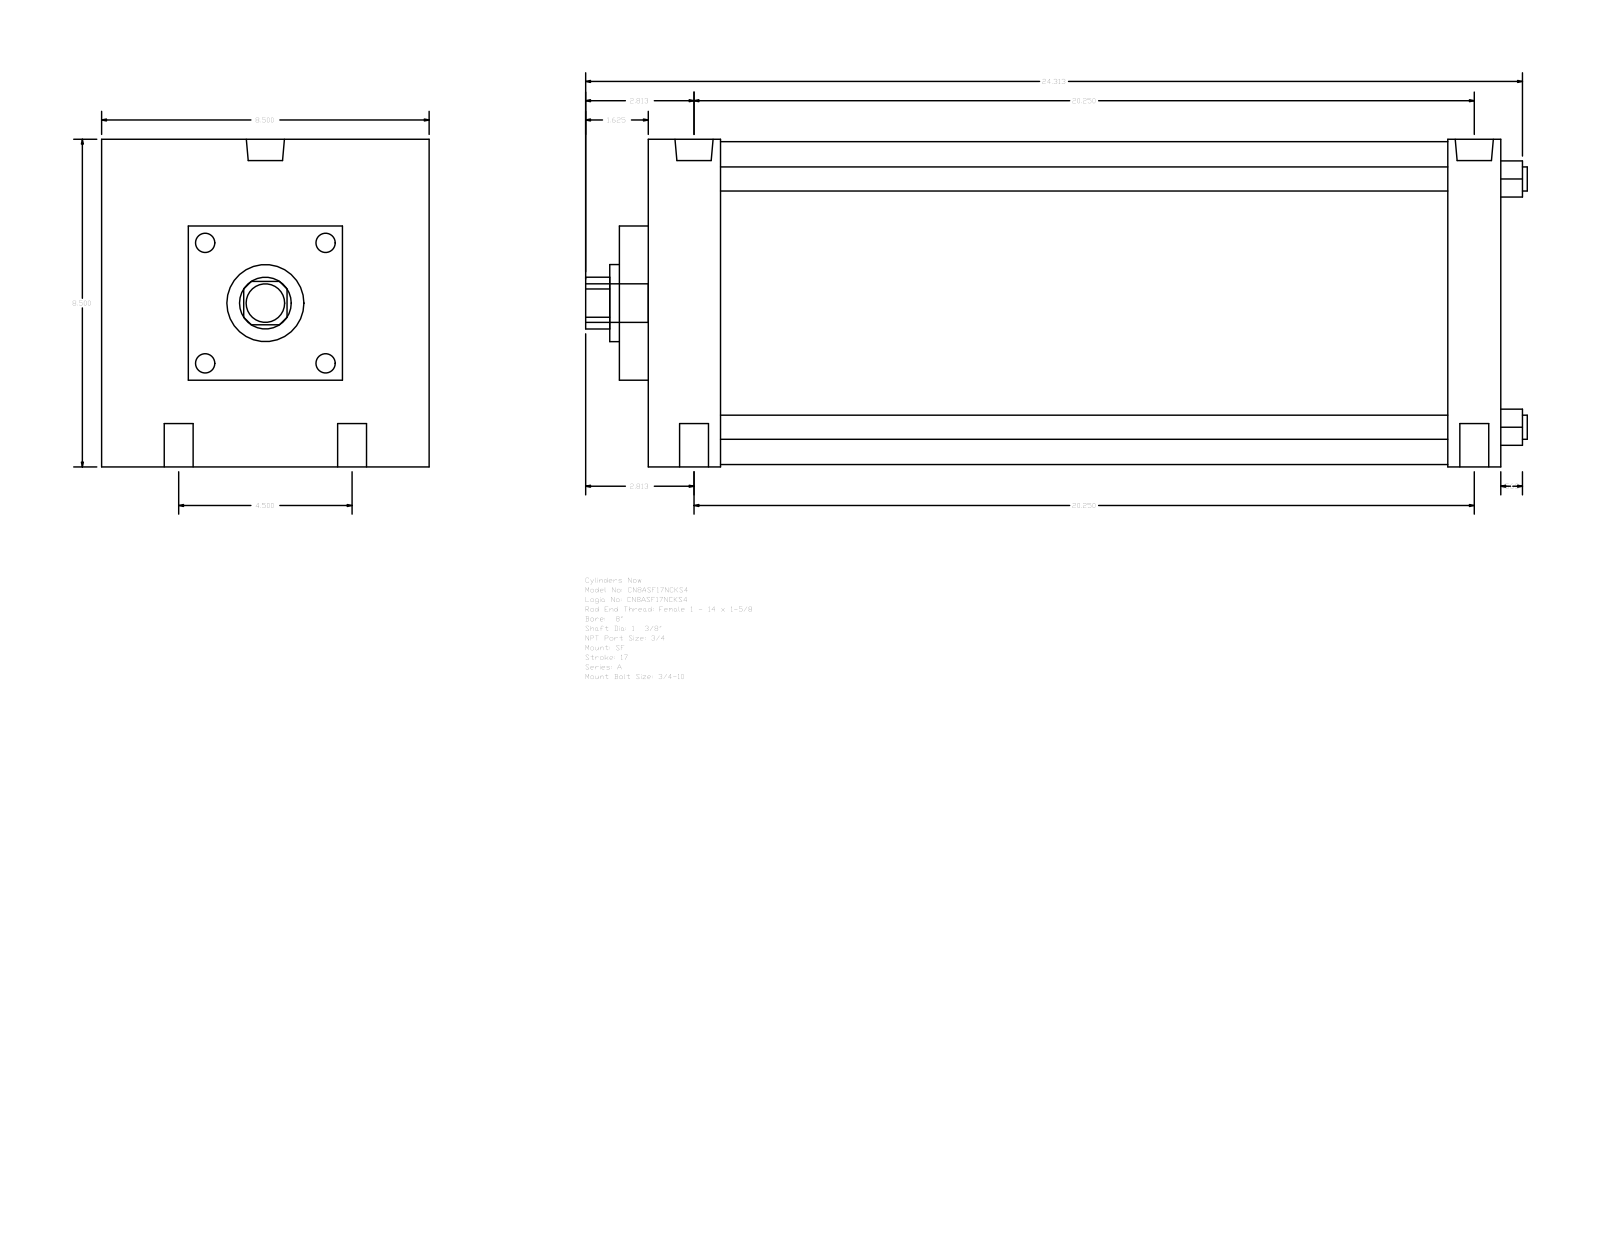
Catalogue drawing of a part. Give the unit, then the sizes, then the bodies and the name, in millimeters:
Units: millimetres
Overall size (bounding box): 620.71 × 215.9 × 215.9
Round holes (diameter × count): ⌀19.05 ×4, ⌀15.08 ×2, ⌀25.12 ×2, ⌀34.92 ×1, ⌀50.8 ×1
Round bosses / shafts (diameter × count): ⌀15.88 ×4, ⌀212.72 ×1, ⌀25.4 ×1
Partial cylindrical surfaces — rounded edges, fillets, slot ends (radius × count): R17.06 ×1
Main face-to-face distances: 561.98, 215.9, 47.63, 527.06, 479.43, 514.35, 34.92, 19.04, 66.67, 546.1
Hole centre spacings: 57.15, 517.52, 514.35, 114.3, 526.9, 501.65
Bodies: 0 solids, 93 faces (67 planar, 26 cylindrical, 0 other)
Part name (STEP PRODUCT): A_SF__0800_1.375
STEP written by: GSSL Pune (CONFIG_CONTROL_DESIGN)
